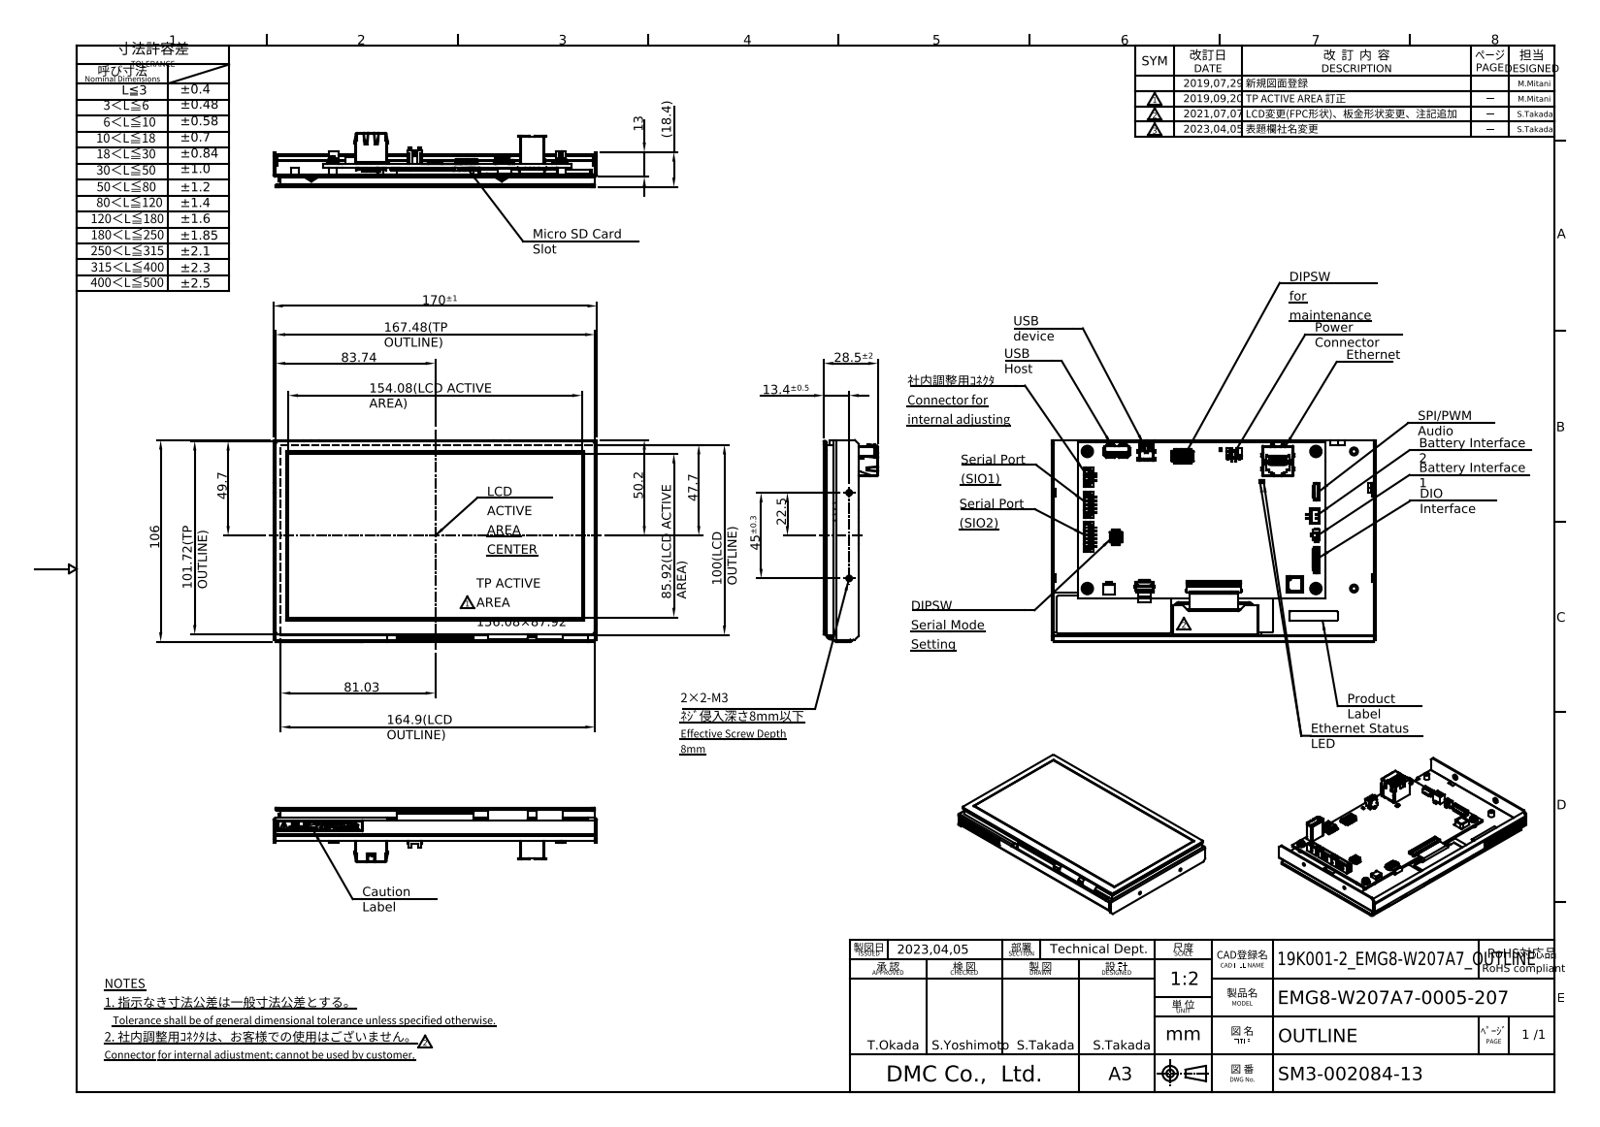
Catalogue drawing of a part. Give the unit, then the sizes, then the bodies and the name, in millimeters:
Units: millimetres
Overall size (bounding box): 170 × 106.2 × 28.47
Round holes (diameter × count): ⌀2.46 ×8, ⌀3.5 ×4, ⌀8 ×4, ⌀1.2 ×2, ⌀0.3 ×1, ⌀1.33 ×1
Round bosses / shafts (diameter × count): ⌀4.2 ×6, ⌀6 ×4, ⌀5.5 ×4, ⌀3.6 ×4, ⌀3 ×4, ⌀4 ×2
Partial cylindrical surfaces — rounded edges, fillets, slot ends (radius × count): R0.1 ×208, R0.15 ×57, R0.2 ×50, R0.5 ×42, R0.25 ×29, R0.3 ×28, R0.13 ×16, R1 ×16
Main face-to-face distances: 3.71, 4.87, 6.37, 1.5, 4.71, 1.66, 1, 4, 8.71, 8.87
Hole centre spacings: 72, 20, 74.73, 120, 139.94, 140, 157.43, 14.55
Volume: 134 259 mm³ · Surface area: 136 195 mm²
Bodies: 1 solid, 6576 faces (5057 planar, 921 cylindrical, 598 other)
Part name (STEP PRODUCT): HP_EMG8-W207A7-0005-207
STEP written by: Autodesk Inventor 2020 (AUTOMOTIVE_DESIGN)
